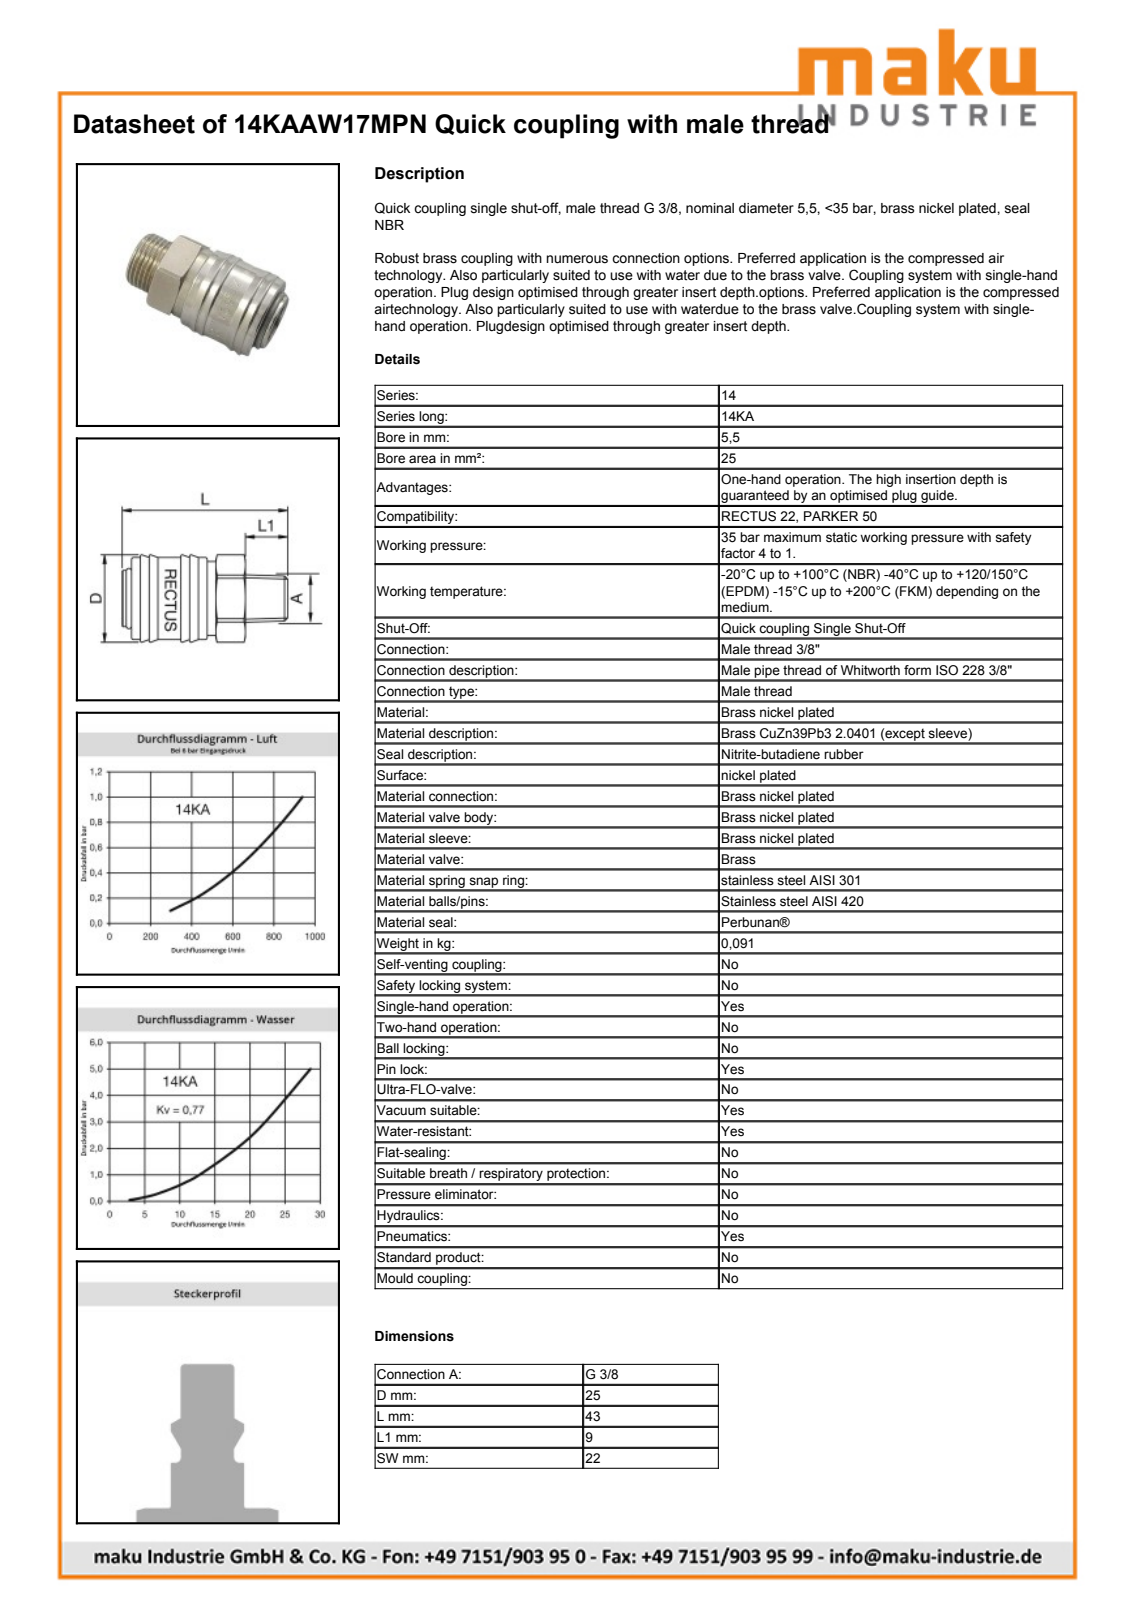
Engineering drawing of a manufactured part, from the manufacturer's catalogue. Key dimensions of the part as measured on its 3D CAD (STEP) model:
Part name (STEP PRODUCT): D109920
STEP written by: Autodesk Inventor 2013 (AUTOMOTIVE_DESIGN)
Units: millimetres
Bodies: 3 solids, 497 faces (211 planar, 58 cylindrical, 228 other)
Overall size (bounding box): 43.6 × 24.8 × 24.8
Volume: 13 756 mm³ · Surface area: 8 333 mm²
Round holes (diameter × count): ⌀14.45 ×1, ⌀16.1 ×1, ⌀17 ×1, ⌀21.1 ×1
Round bosses / shafts (diameter × count): ⌀23.3 ×1, ⌀21 ×1, ⌀18 ×1, ⌀16.67 ×1, ⌀16.65 ×1, ⌀15.95 ×1, ⌀14.95 ×1, ⌀13.22 ×1
Partial cylindrical surfaces — rounded edges, fillets, slot ends (radius × count): R11.55 ×1, R12.4 ×1
Main face-to-face distances: 9, 2.65, 22, 43.6, 40.95, 34.6, 31.95, 11.1, 23.5, 20.85
